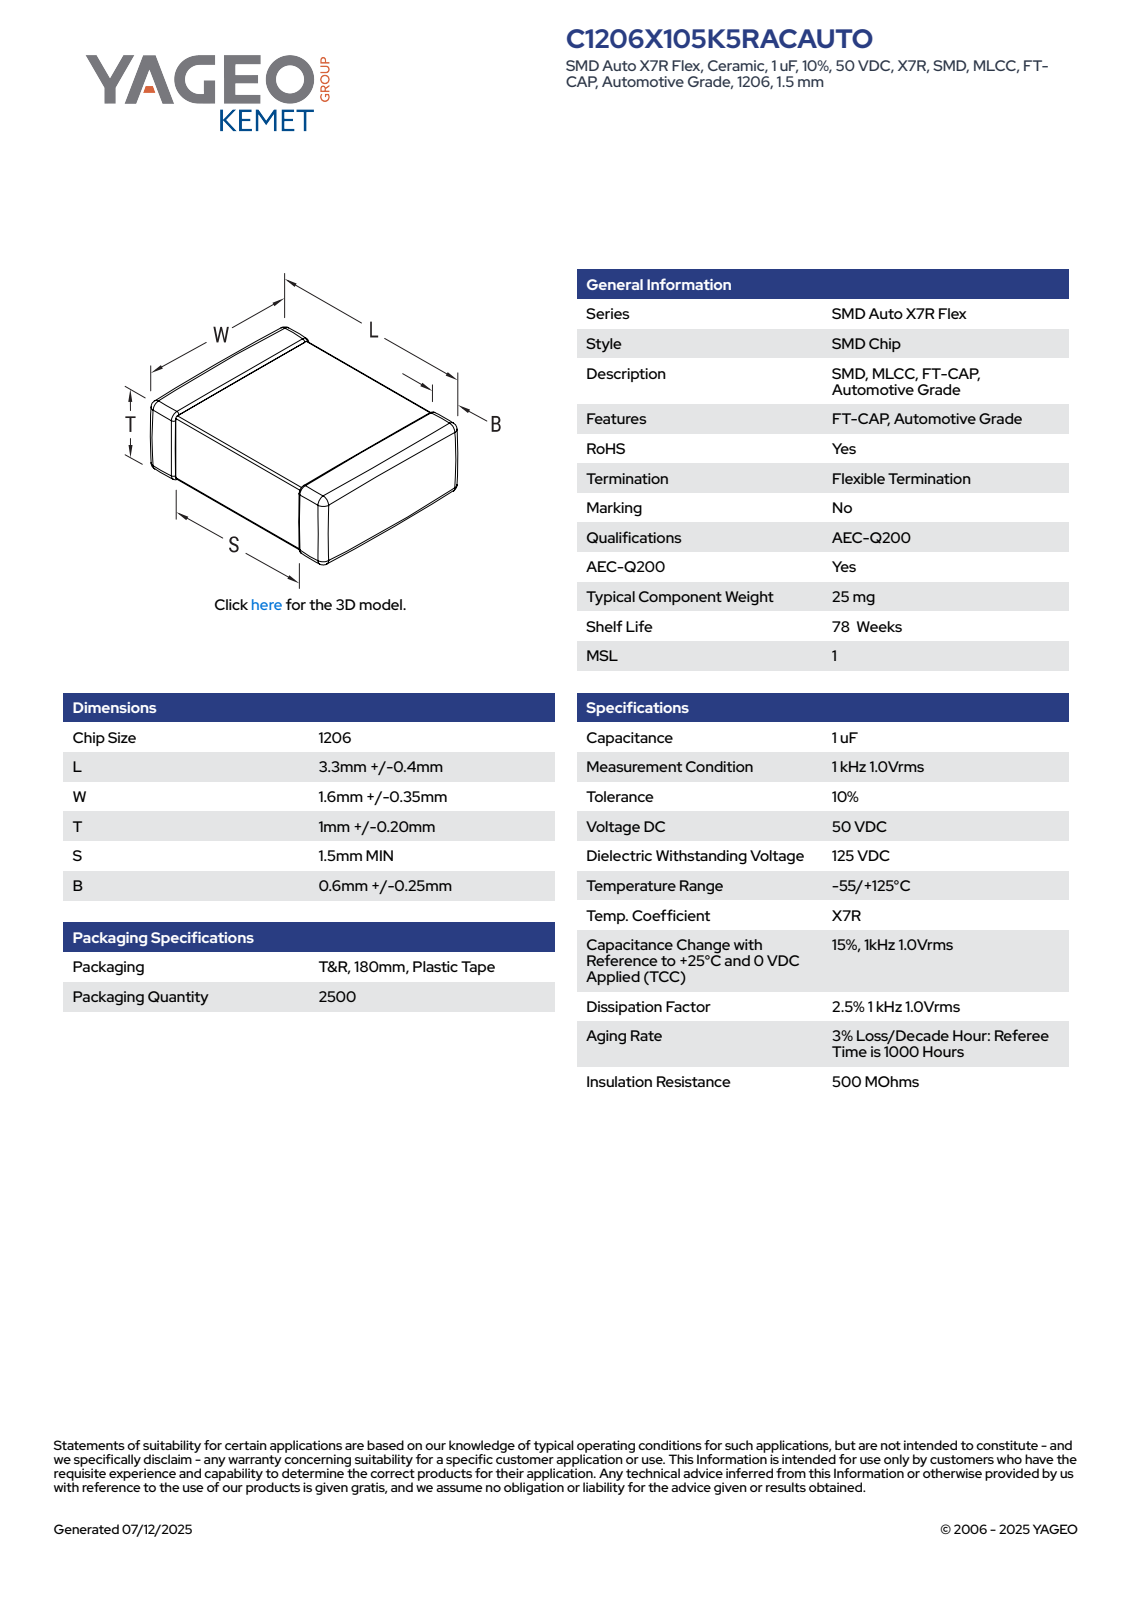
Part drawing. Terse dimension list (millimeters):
name: CCS_CCSTDNOS_1206_L3.7W1.95T1.2B0.85
written by: SolidWorks 2014 (AUTOMOTIVE_DESIGN)
unit: mm
bodies: 4 solids, 125 faces (71 planar, 38 cylindrical, 16 other)
size: 3.7 × 1.95 × 1.2
volume: 8 mm³; area: 28 mm²
face distances: 1.16, 1.12, 1.91, 1.2, 3.7, 1.87, 1.95, 0.86, 0.82, 1.05
